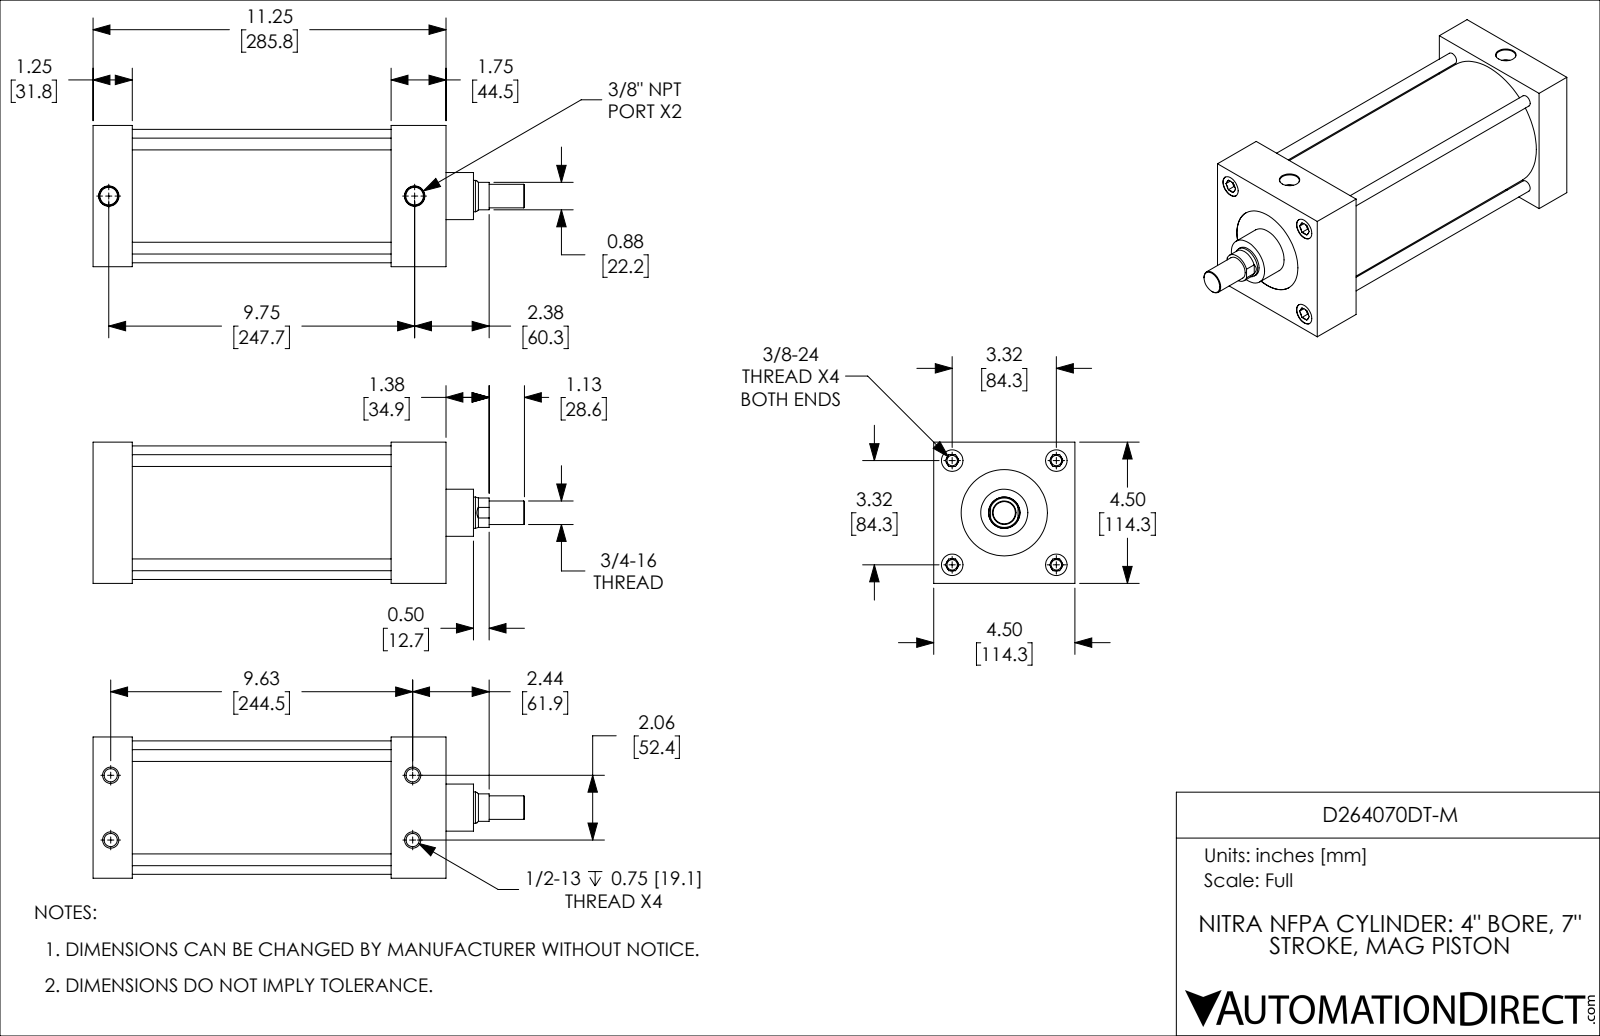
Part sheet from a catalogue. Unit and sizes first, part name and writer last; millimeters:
Units: millimetres
Overall size (bounding box): 349.3 × 114.3 × 114.3
Round holes (diameter × count): ⌀8.4 ×4, ⌀10.7 ×4, ⌀17.4 ×4, ⌀14.3 ×2, ⌀25.4 ×1, ⌀69.9 ×1, ⌀101.6 ×1
Round bosses / shafts (diameter × count): ⌀9.5 ×4, ⌀108 ×1, ⌀101.6 ×1, ⌀38.1 ×1, ⌀25.4 ×1, ⌀19.1 ×1
Partial cylindrical surfaces — rounded edges, fillets, slot ends (radius × count): R11.9 ×1
Main face-to-face distances: 31.8, 114.3, 241.3, 209.6, 285.8, 254, 44.5, 63.5, 177.8, 222.3
Hole centre spacings: 59.6, 84.3, 247.4, 26.2, 119.3, 244.5, 250, 26.3
Volume: 1 622 000 mm³ · Surface area: 315 800 mm²
Bodies: 2 solids, 198 faces (58 planar, 62 cylindrical, 78 other)
Part name (STEP PRODUCT): D264070DT-M_BODY; D264070DT-M_PISTON_KK1; D264070DT-M
STEP written by: SolidWorks 2019 (CONFIG_CONTROL_DESIGN)
